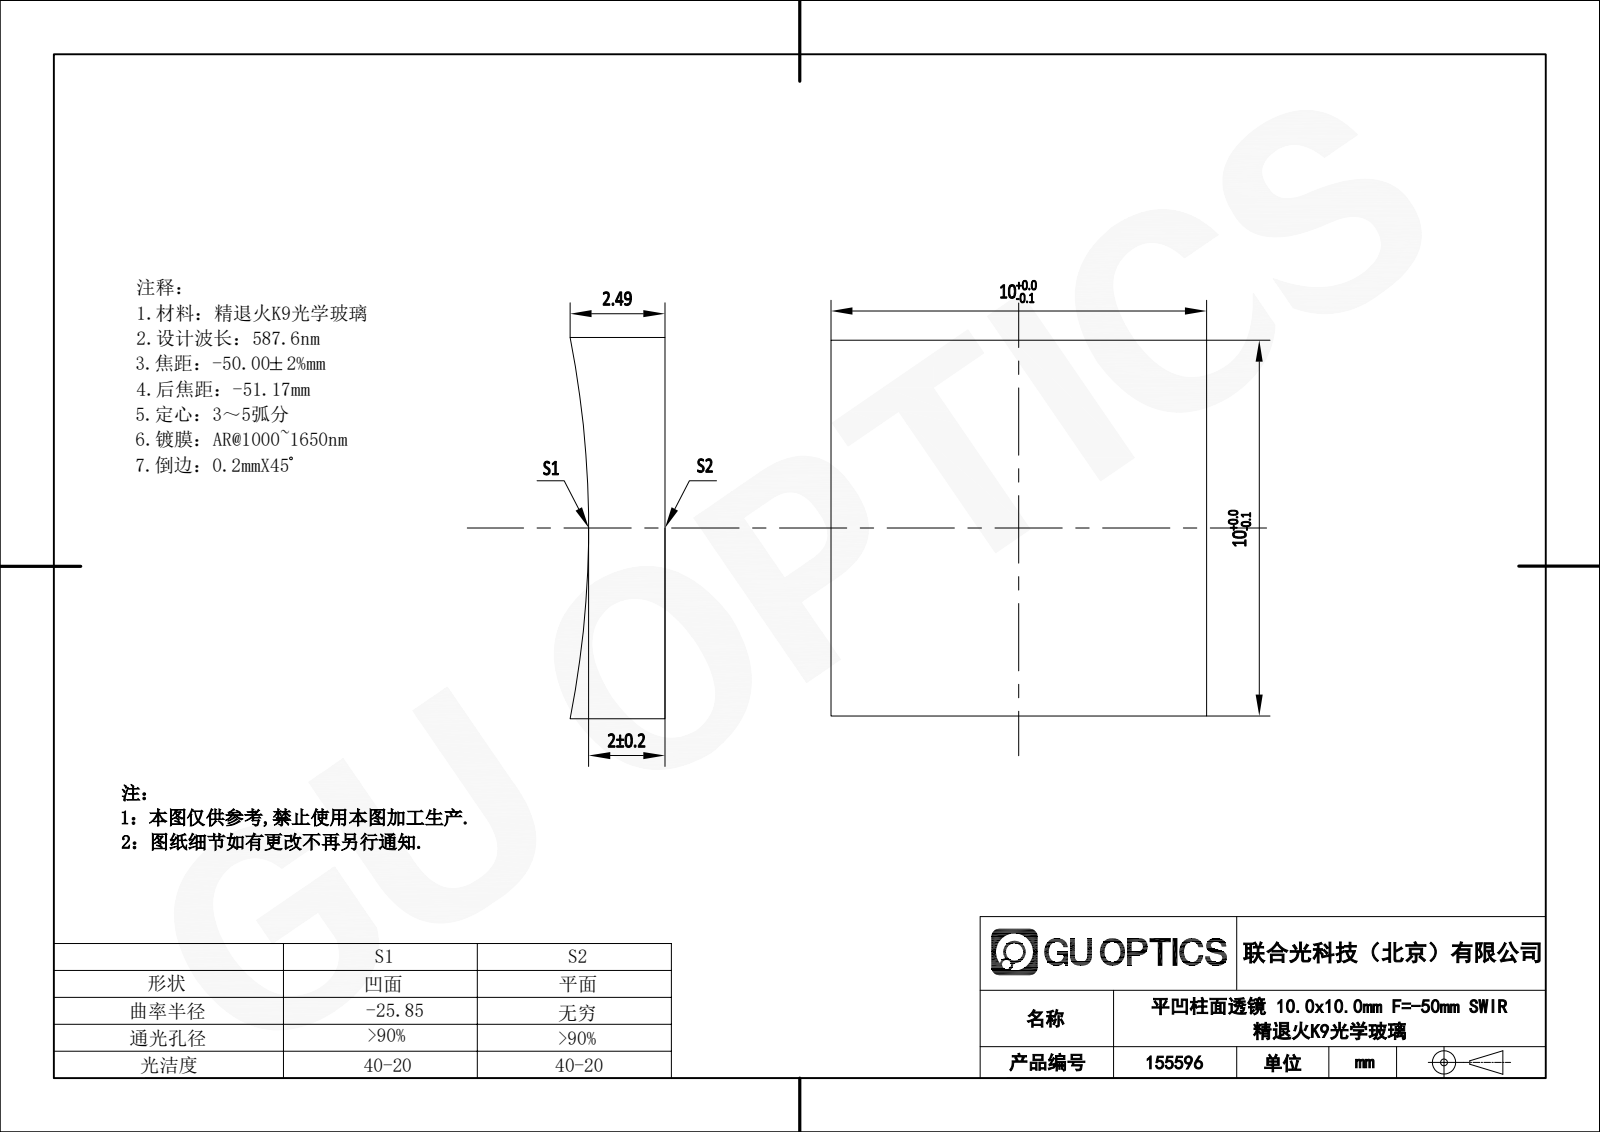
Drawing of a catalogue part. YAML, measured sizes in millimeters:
part_name: "155566"
step_written_by: "SolidWorks 2020 (CONFIG_CONTROL_DESIGN)"
units: millimeters
bodies: {solids: 1, faces: 6, planar: 5, cylindrical: 1, other: 0}
overall_size: [10, 10, 2.49]
volume: 216
surface_area: 294
partial_cylinders:
  - {radius: 25.85, count: 1}
face_to_face_distances: [10]
